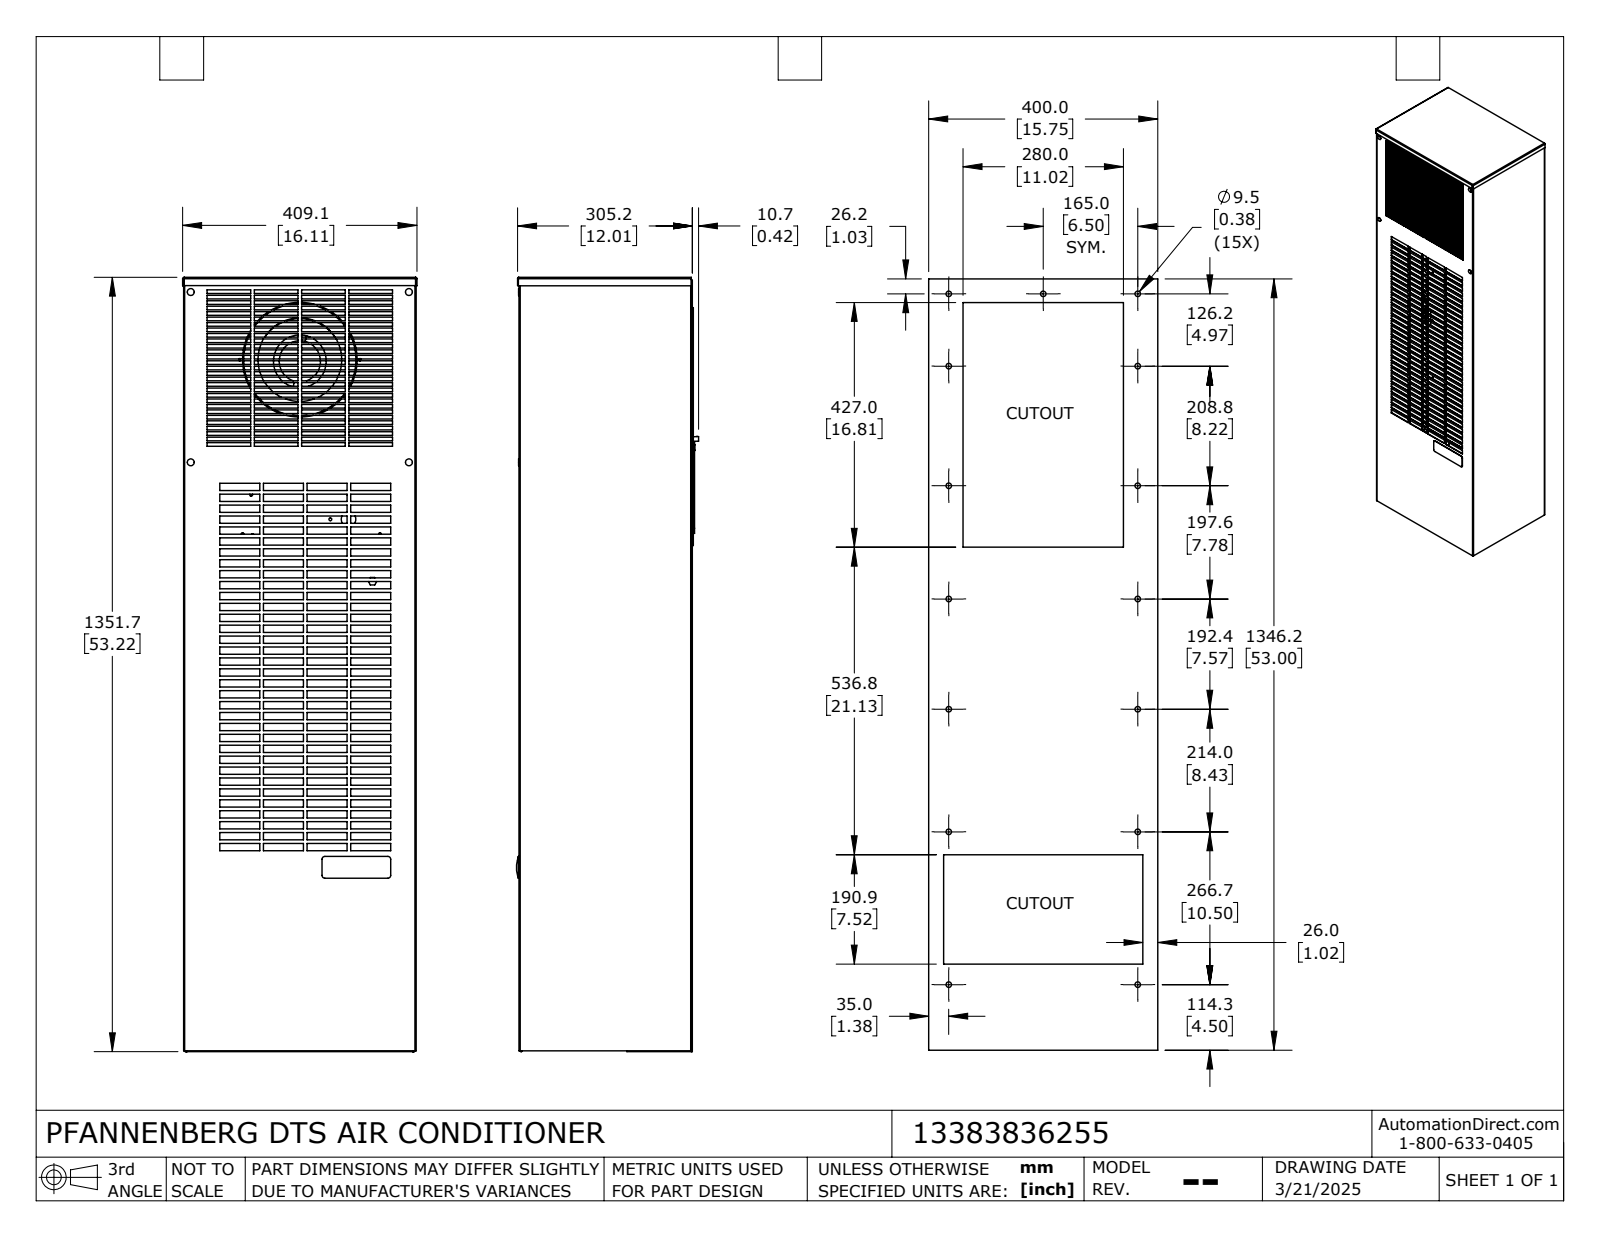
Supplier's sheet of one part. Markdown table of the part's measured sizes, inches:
| quantity | value |
| --- | --- |
| part name | 13383836255_Default |
| STEP written by | SolidWorks 2024 (CONFIG_CONTROL_DESIGN) |
| units | inches |
| bodies | 20 solids, 3087 faces (2071 planar, 908 cylindrical, 108 other) |
| overall size | 53.217 × 16.106 × 12.518 |
| volume | 433.9 in³ |
| surface area | 10 861 in² |
| round holes (diameter × count) | 0.165 × 64, 0.165 × 18, 0.157 × 15, 0.375 × 15, 0.165 × 10, 0.197 × 8, 0.25 × 8, 0.236 × 7, 0.13 × 5, 0.177 × 4, 0.217 × 4, 0.022 × 2 |
| round bosses / shafts (diameter × count) | 0.079 × 5, 0.472 × 4, 0.276 × 2, 0.031 × 2, 8.858 × 1, 8.78 × 1, 5.866 × 1, 3.622 × 1 |
| partial cylindrical surfaces (radius × count) | 0.125 × 140, 0.031 × 23, 0.079 × 19, 0.031 × 8, 0.079 × 8, 0.197 × 8, 0.05 × 7, 0.118 × 5 |
| main face-to-face distances | 0.048, 0.048, 15.941, 0.166, 15.99, 15.893, 4.362, 4.528, 11.923, 7.561 |
| hole center spacings | 0.02, 12.992, 4, 8, 8.75, 16, 20.611, 0.02 |
